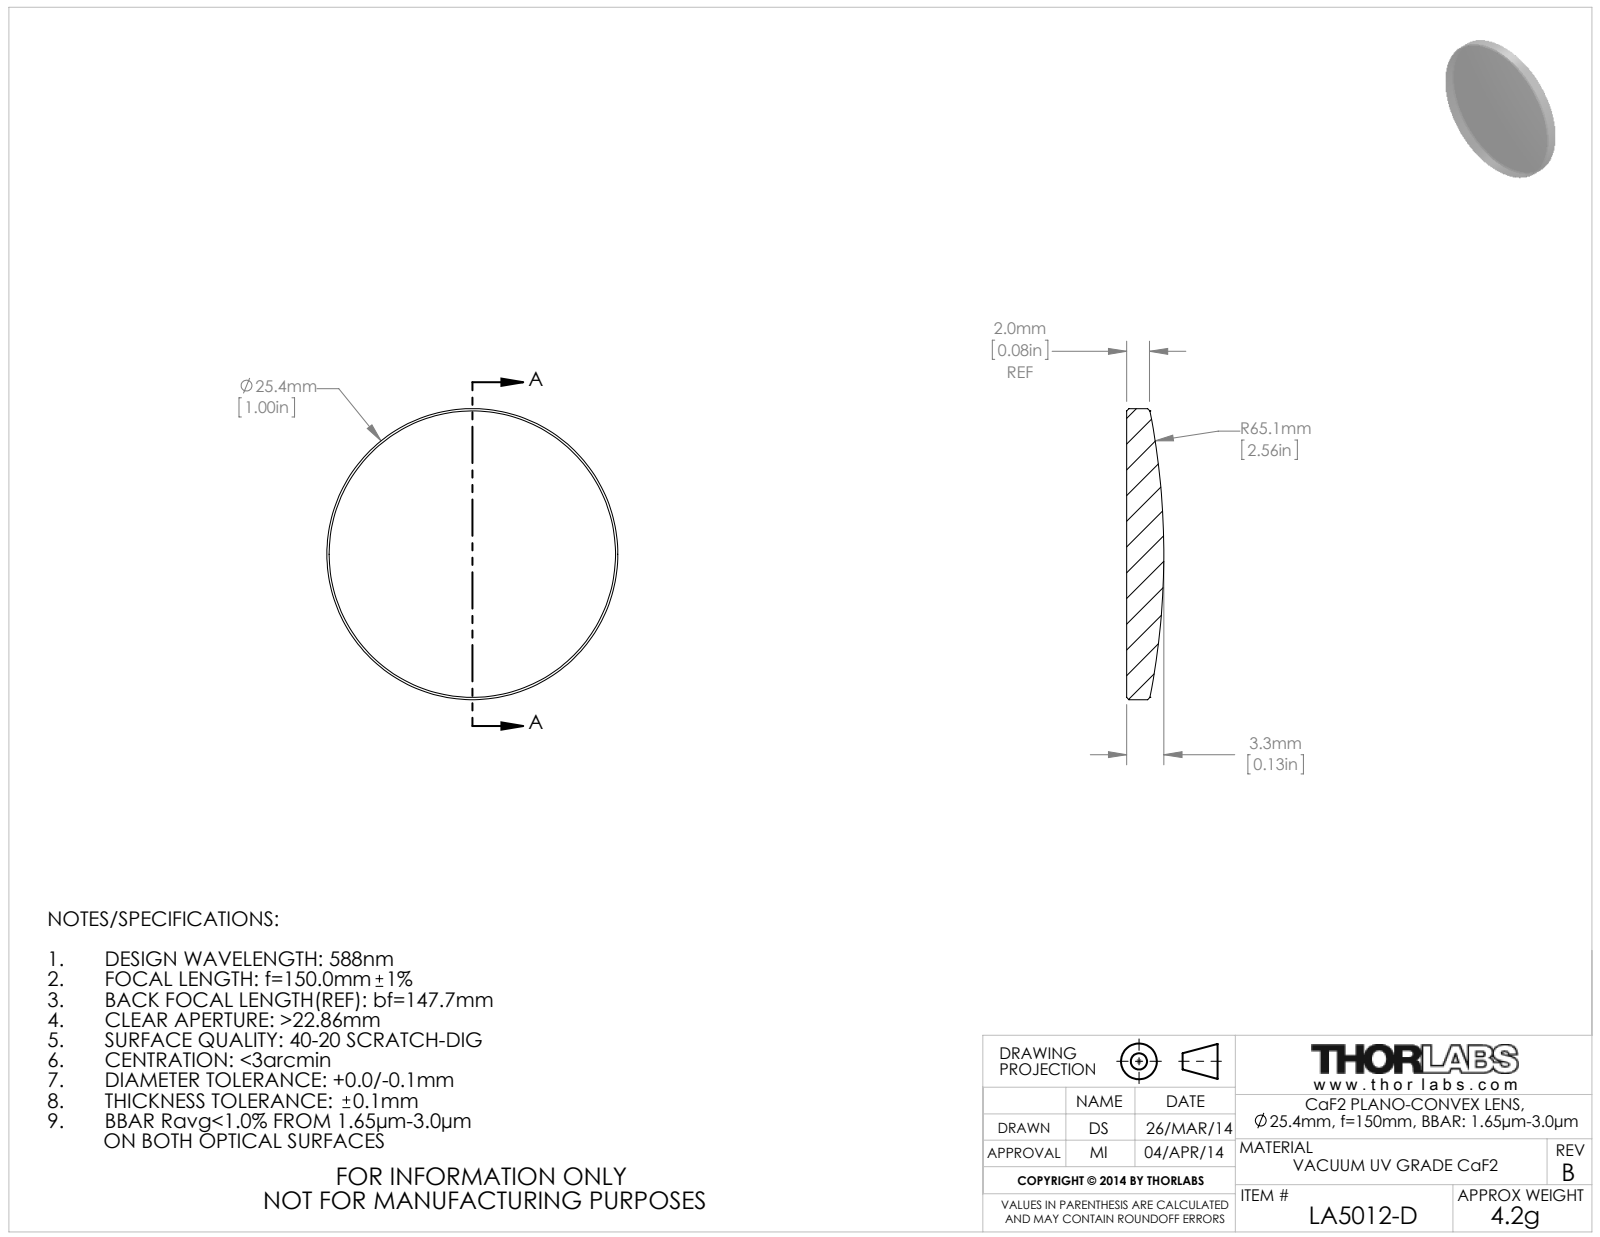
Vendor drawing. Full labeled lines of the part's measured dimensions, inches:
Part name (STEP PRODUCT): 22963-E0W
STEP written by: SolidWorks 2011 (AUTOMOTIVE_DESIGN)
Units: inches
Bodies: 0 solids, 5 faces (1 planar, 2 cylindrical, 2 other)
Overall size (bounding box): 1 × 1 × 0.128
Round bosses / shafts (diameter × count): ⌀1 ×1
